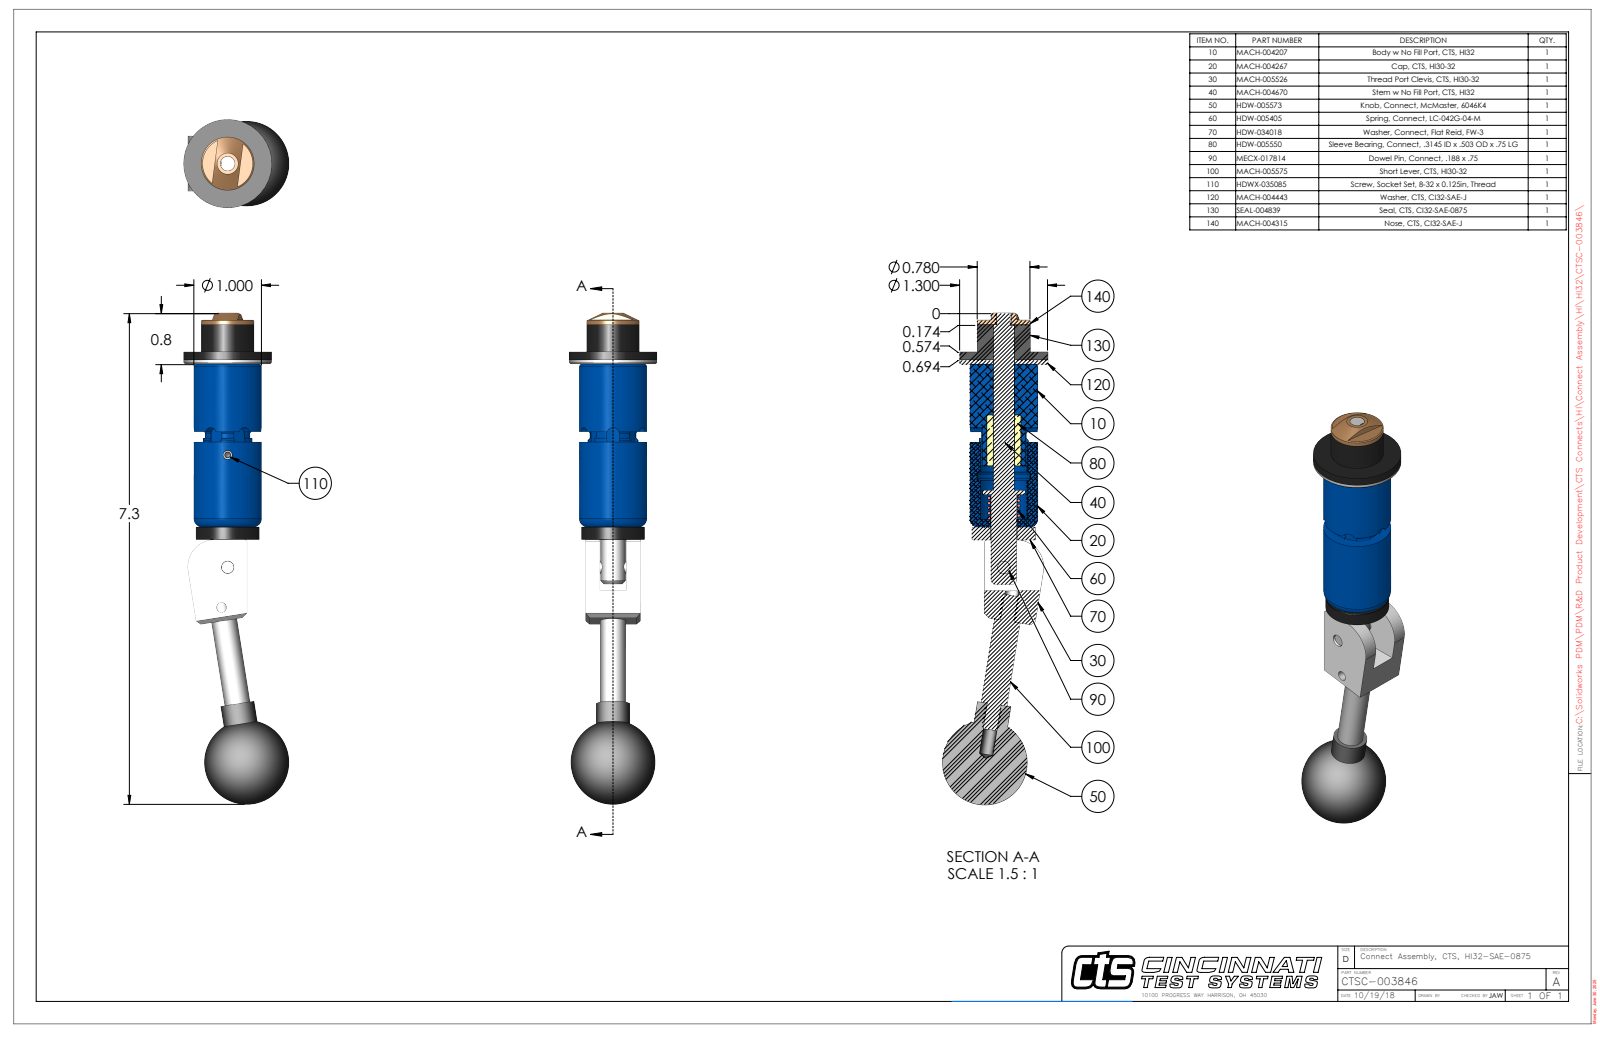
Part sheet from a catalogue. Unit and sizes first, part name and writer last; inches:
Units: inches
Overall size (bounding box): 7.256 × 1.555 × 1.3
Round holes (diameter × count): ⌀0.201 ×2, ⌀0.136 ×1, ⌀0.15 ×1, ⌀0.189 ×1, ⌀0.213 ×1, ⌀0.31 ×1, ⌀0.314 ×1, ⌀0.316 ×1, ⌀0.385 ×1, ⌀0.392 ×1, ⌀0.688 ×1
Round bosses / shafts (diameter × count): ⌀0.25 ×2, ⌀0.201 ×2, ⌀1.3 ×1, ⌀1 ×1, ⌀0.936 ×1, ⌀0.78 ×1, ⌀0.5 ×1, ⌀0.38 ×1
Partial cylindrical surfaces — rounded edges, fillets, slot ends (radius × count): R0.093 ×6, R0.029 ×2, R0.375 ×1, R0.4 ×1, R0.465 ×1
Main face-to-face distances: 0.06, 0.21, 0.602, 2.465, 2.405, 0.52, 0.58, 2.985, 0.812, 0.4
Hole centre spacings: 0.599, 1.658, 2.252
Volume: 4.223 in³ · Surface area: 37.33 in²
Bodies: 9 solids, 268 faces (100 planar, 110 cylindrical, 58 other)
Part name (STEP PRODUCT): CTSC-003846
STEP written by: SolidWorks 2023 (AUTOMOTIVE_DESIGN)
